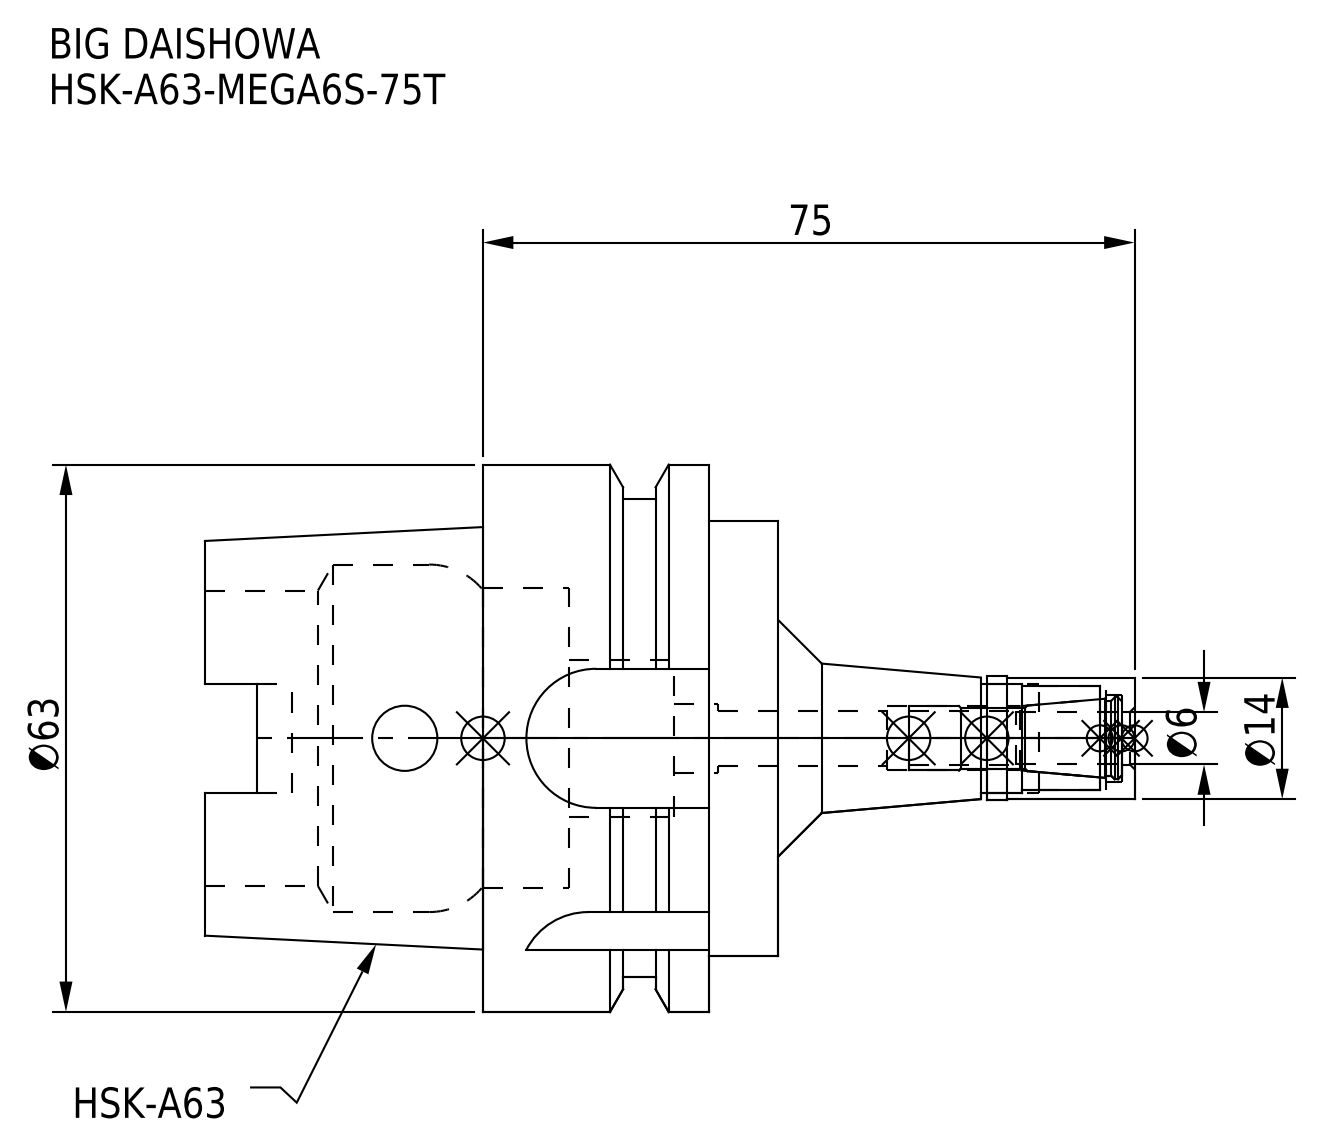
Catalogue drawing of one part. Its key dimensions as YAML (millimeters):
part_name: "HSK-A63-MEGA6S-75T_1.stp; MGN6S_1.stp; HSK-A63-MEGA6S-75T; HA63MS06075T-060_ASM.stp (+3 more)"
step_written_by: "SolidWorks 2019 (CONFIG_CONTROL_DESIGN)"
units: millimeters
bodies: {solids: 2, faces: 122, planar: 47, cylindrical: 53, other: 22}
overall_size: [107, 63, 63]
volume: 103434
surface_area: 27713
round_holes:
  - {diameter: 6.1, count: 1}
  - {diameter: 6.4, count: 1}
  - {diameter: 7.4, count: 1}
  - {diameter: 7.5, count: 1}
  - {diameter: 8, count: 1}
  - {diameter: 10, count: 1}
  - {diameter: 12, count: 1}
  - {diameter: 12.5, count: 1}
  - {diameter: 18, count: 1}
  - {diameter: 34, count: 1}
  - {diameter: 34.5, count: 1}
  - {diameter: 40, count: 1}
round_bosses_or_shafts:
  - {diameter: 63, count: 1}
  - {diameter: 55, count: 1}
  - {diameter: 50, count: 1}
  - {diameter: 14.3, count: 1}
  - {diameter: 14, count: 1}
partial_cylinders:
  - {radius: 2.88, count: 4}
  - {radius: 8, count: 4}
face_to_face_distances: [34, 26, 8, 24.05, 16.05, 9.95, 32, 58, 66, 41.95]
